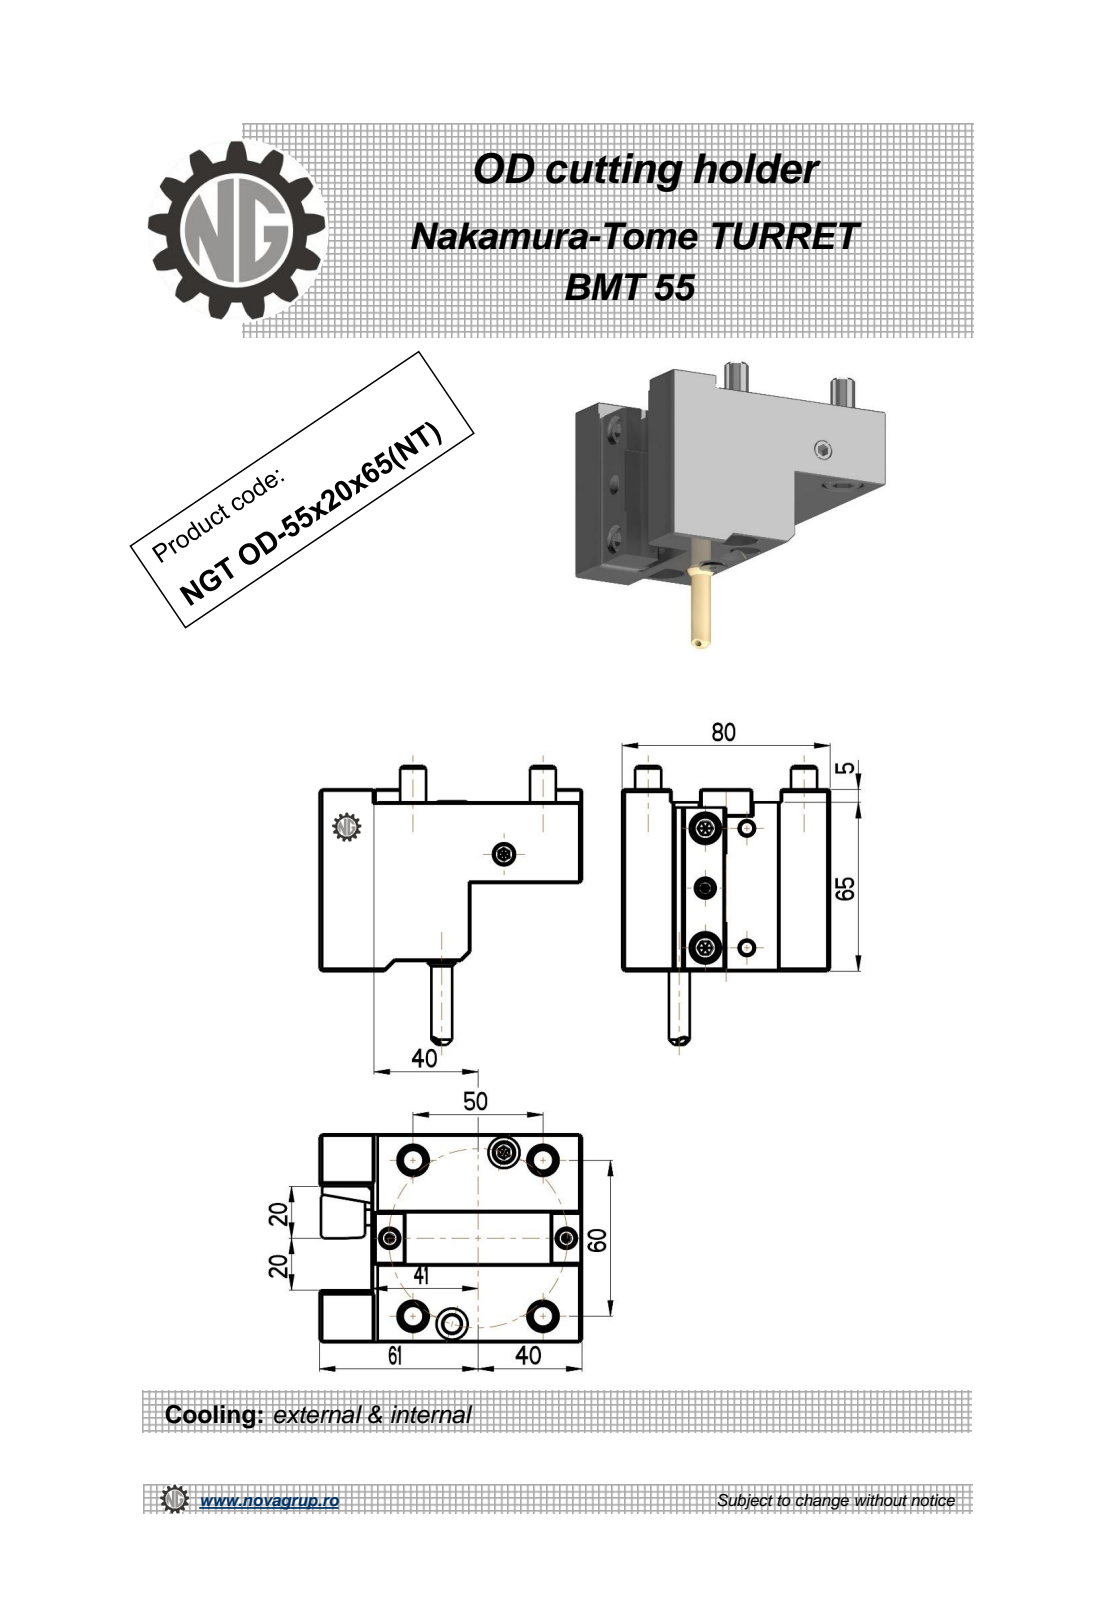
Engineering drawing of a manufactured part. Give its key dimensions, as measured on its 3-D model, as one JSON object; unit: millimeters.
{"part_name": "NGT_OD_55_20_65_NT", "step_written_by": "PRO/ENGINEER BY PARAMETRIC TECHNOLOGY CORPORATION, 2010280 (CONFIG_CONTROL_DESIGN)", "units": "millimeters", "bodies": {"solids": 1, "faces": 210, "planar": 134, "cylindrical": 43, "other": 33}, "overall_size": [107.34, 101, 80], "volume_mm3": 372132, "surface_area_mm2": 45477, "round_holes": [[12, 2], [3, 1], [5, 1], [6.8, 1]], "round_bosses_or_shafts": [[10, 4], [6, 3], [11.2, 1], [8, 1]], "partial_cylinders_radius": [[0.22, 6], [0.41, 6], [1, 1]], "face_to_face_distances": [80, 20, 31, 30, 60, 10, 101, 5, 81, 58], "hole_center_spacings": [28.3, 51.16, 68.96]}
